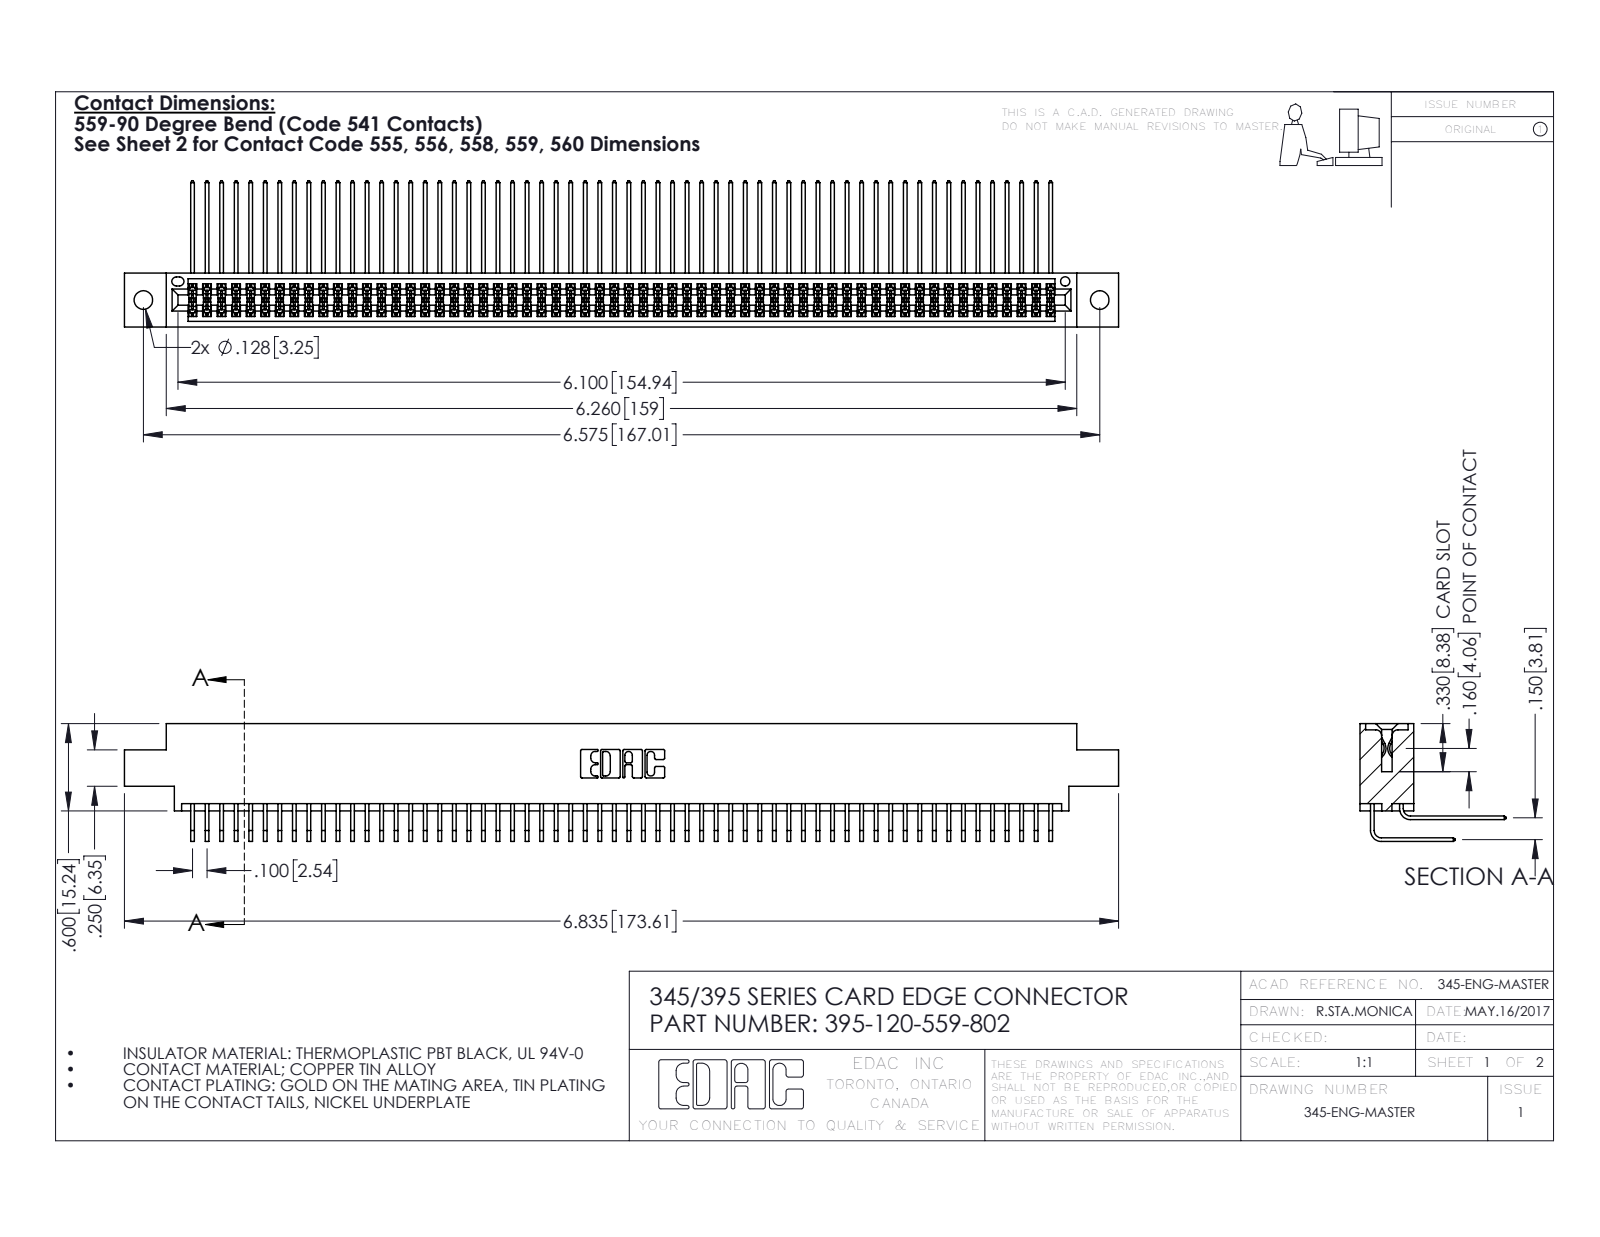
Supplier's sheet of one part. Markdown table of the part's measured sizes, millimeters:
| quantity | value |
| --- | --- |
| part name | 345 Part_0.170 Offset - 0.128 Dia; 345-292-001_558 559 Tail - 1; 395-120-559-802; 345-292-001_559 Tail - 2 |
| STEP written by | SolidWorks 2016 (CONFIG_CONTROL_DESIGN) |
| units | millimeters |
| bodies | 121 solids, 6370 faces (4284 planar, 2086 cylindrical, 0 other) |
| overall size | 173.6 × 25.5 × 20.5 |
| volume | 17 570 mm³ |
| surface area | 29 450 mm² |
| round holes (diameter × count) | 3.3 × 2, 1.6 × 1 |
| partial cylindrical surfaces (radius × count) | 0.2 × 181, 0.3 × 22, 0.2 × 6, 0.8 × 6, 0.7 × 3, 0.4 × 2, 0.5 × 2, 0.6 × 2 |
| main face-to-face distances | 1.8, 7.6, 9.4, 5.1, 2.5, 6.9, 0.6, 5.7, 4.4, 3.8 |
| hole center spacings | 6.9, 161, 167 |
